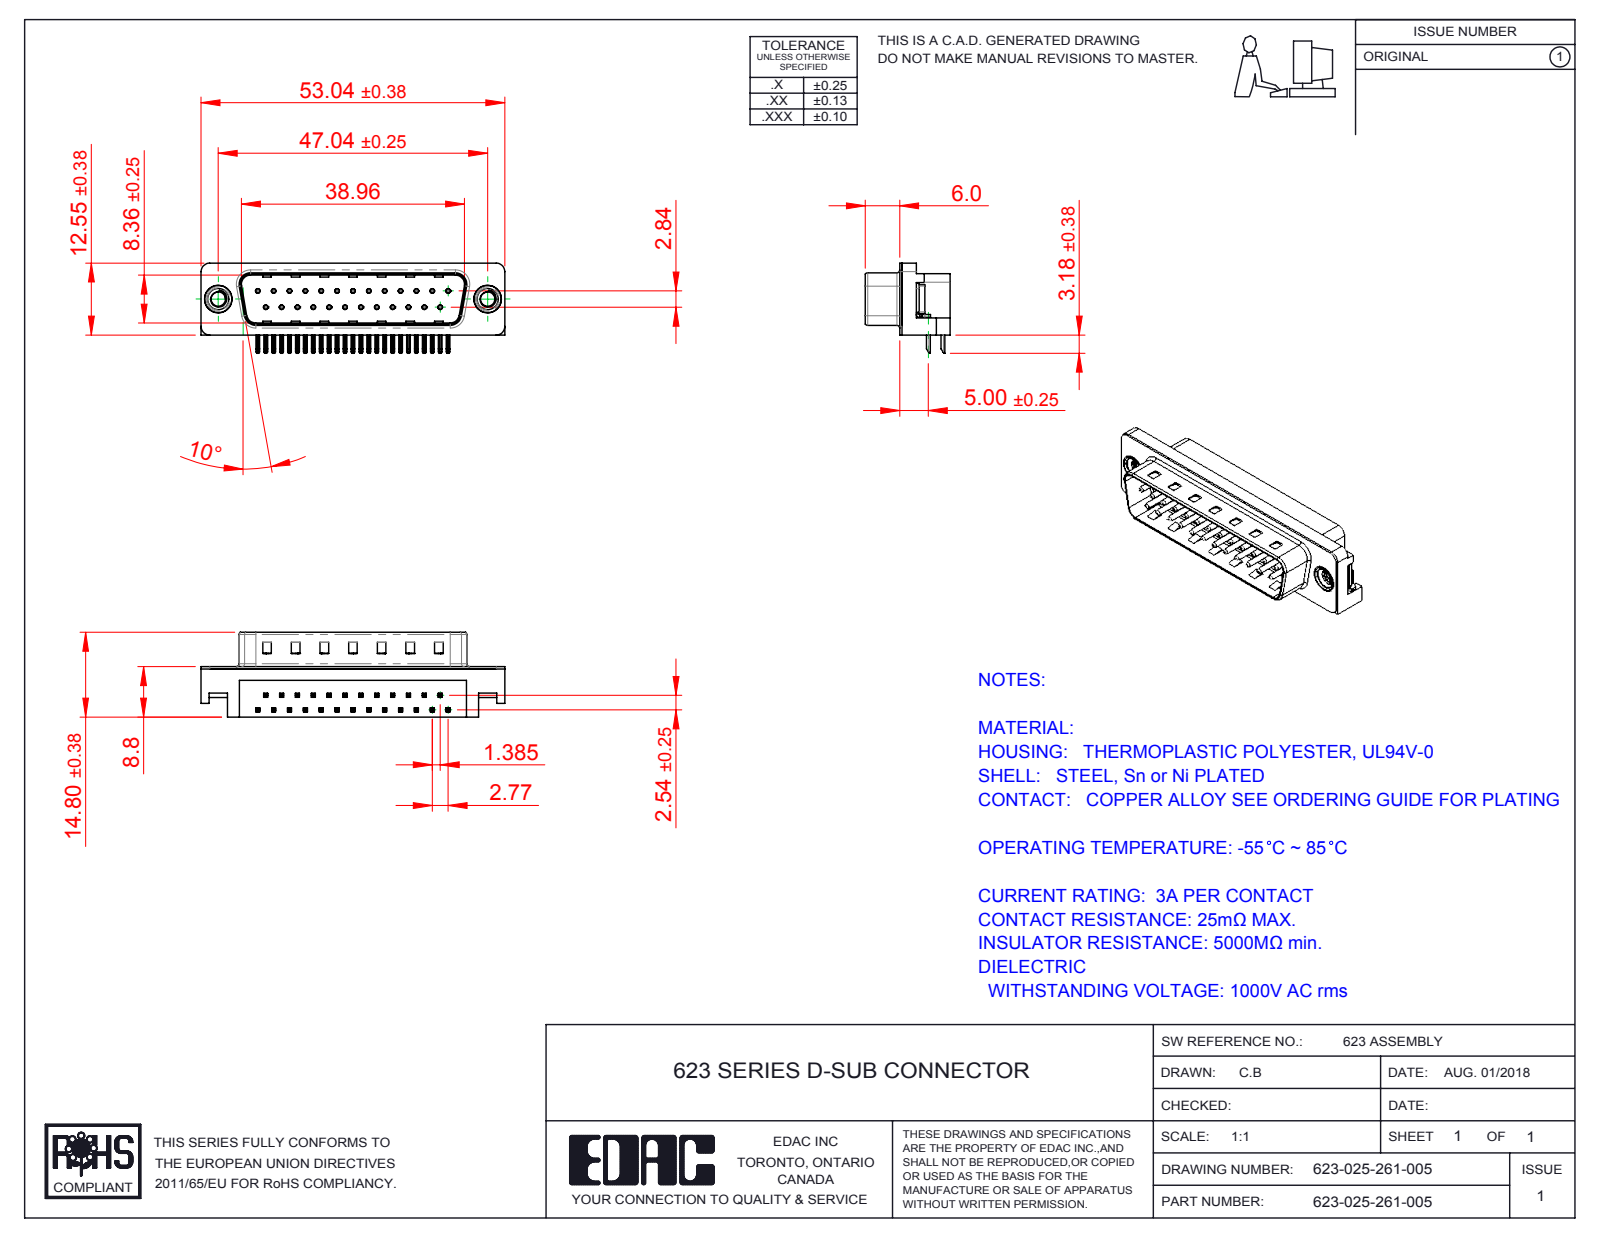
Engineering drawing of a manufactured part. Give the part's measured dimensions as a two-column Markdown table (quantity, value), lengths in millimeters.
| quantity | value |
| --- | --- |
| part name | 623 M3 Threaded Rivet; 623-025-261-005; 623 Shell_25 Socket; 623 Contact Top (+3 more) |
| STEP written by | SolidWorks 2016 (CONFIG_CONTROL_DESIGN) |
| units | millimeters |
| bodies | 31 solids, 2253 faces (1405 planar, 653 cylindrical, 195 other) |
| overall size | 53.04 × 15.73 × 14.8 |
| volume | 4 719 mm³ |
| surface area | 6 720 mm² |
| round holes (diameter × count) | 0.35 × 25, 0.8 × 25, 2.5 × 2, 4 × 2, 4.8 × 2, 5 × 2 |
| round bosses / shafts (diameter × count) | 0.75 × 25, 4.9 × 2, 4.75 × 2, 3.9 × 2 |
| partial cylindrical surfaces (radius × count) | 0.25 × 108, 0.12 × 50, 1 × 16, 0.5 × 9, 1.5 × 7, 0.9 × 4, 1.6 × 4, 2 × 4 |
| main face-to-face distances | 0.4, 8.4, 2.1, 1.7, 8.76, 10.46, 10.86, 10.35, 8.8, 5.9 |
| hole center spacings | 3.16, 2.77, 11.08, 5.54, 8.31, 5.03, 13.85, 7.48 |
